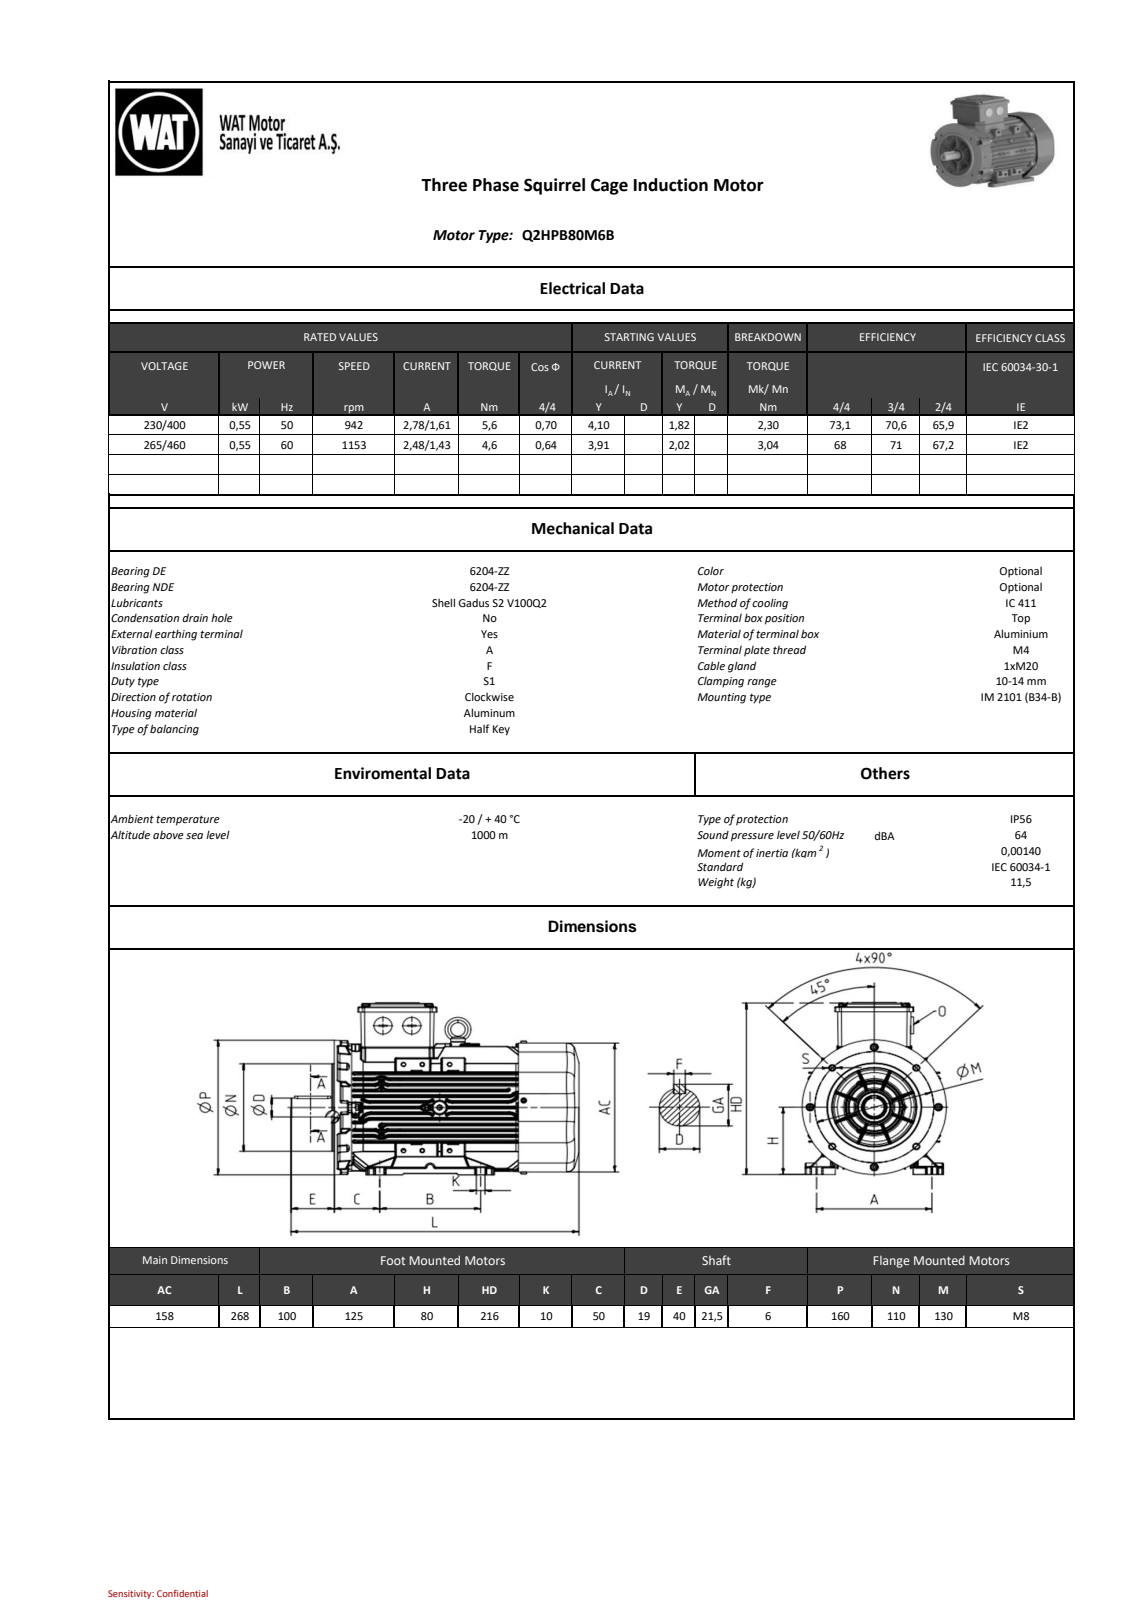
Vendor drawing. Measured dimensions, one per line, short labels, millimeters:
name: model1
written by: SIEMENS PLM Software NX2206.8101 (AUTOMOTIVE_DESIGN)
unit: mm
bodies: 0 solids, 6183 faces (1265 planar, 2505 cylindrical, 2413 other)
size: 268 × 215.5 × 160
holes: 2× ⌀4.6, 1× ⌀5, 1× ⌀8, 1× ⌀57
bosses: 8× ⌀6, 2× ⌀21.38, 1× ⌀146.5, 1× ⌀110, 1× ⌀61, 1× ⌀24.07, 1× ⌀20.2, 1× ⌀20
rounds: 689× R1, 605× R0.5, 337× R0.8, 93× R2, 36× R1.5, 25× R5, 16× R1.45, 14× R3
face distances: 1, 157, 41.96, 10.36, 156.98, 86, 18, 20.98, 10.49, 52.32
hole spacings: 70.94
